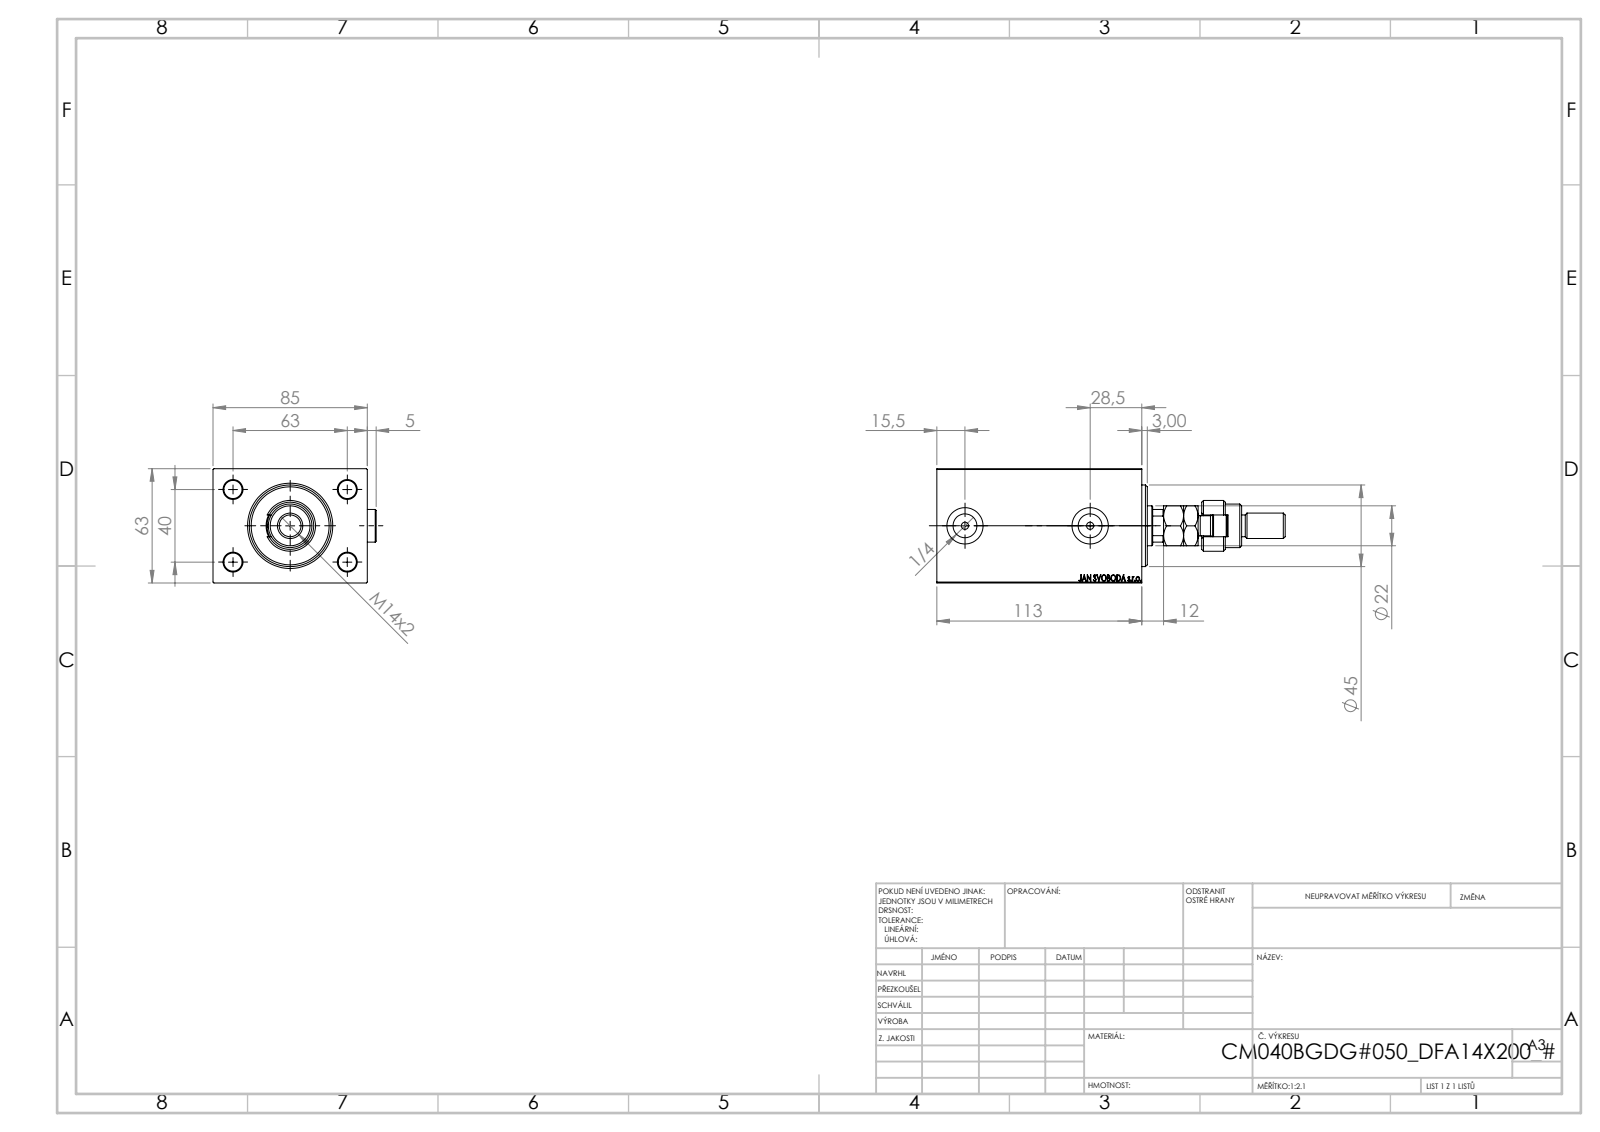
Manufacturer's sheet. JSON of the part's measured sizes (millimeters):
{"part_name": "MFA; Zatka_OIL_PORT; V450CM_VC_B; V450CM_B_VCP (+2 more)", "step_written_by": "SolidWorks 2019 (CONFIG_CONTROL_DESIGN)", "units": "millimeters", "bodies": {"solids": 7, "faces": 1020, "planar": 463, "cylindrical": 83, "other": 474}, "overall_size": [192, 89.9, 63], "volume_mm3": 569421, "surface_area_mm2": 92824, "round_holes": [[10, 4], [4, 2], [13.16, 2], [20, 2], [12.5, 1], [22, 1], [25.5, 1], [26.5, 1], [40, 1], [42, 1], [45, 1]], "round_bosses_or_shafts": [[18, 3], [28, 1], [24, 1], [14, 1], [12, 1], [11, 1]], "partial_cylinders_radius": [[9.75, 1], [10.5, 1]], "face_to_face_distances": [63, 85, 12, 101, 113, 84.9, 3, 89, 51, 15], "hole_center_spacings": [37.31, 40, 63, 74.63, 69]}
